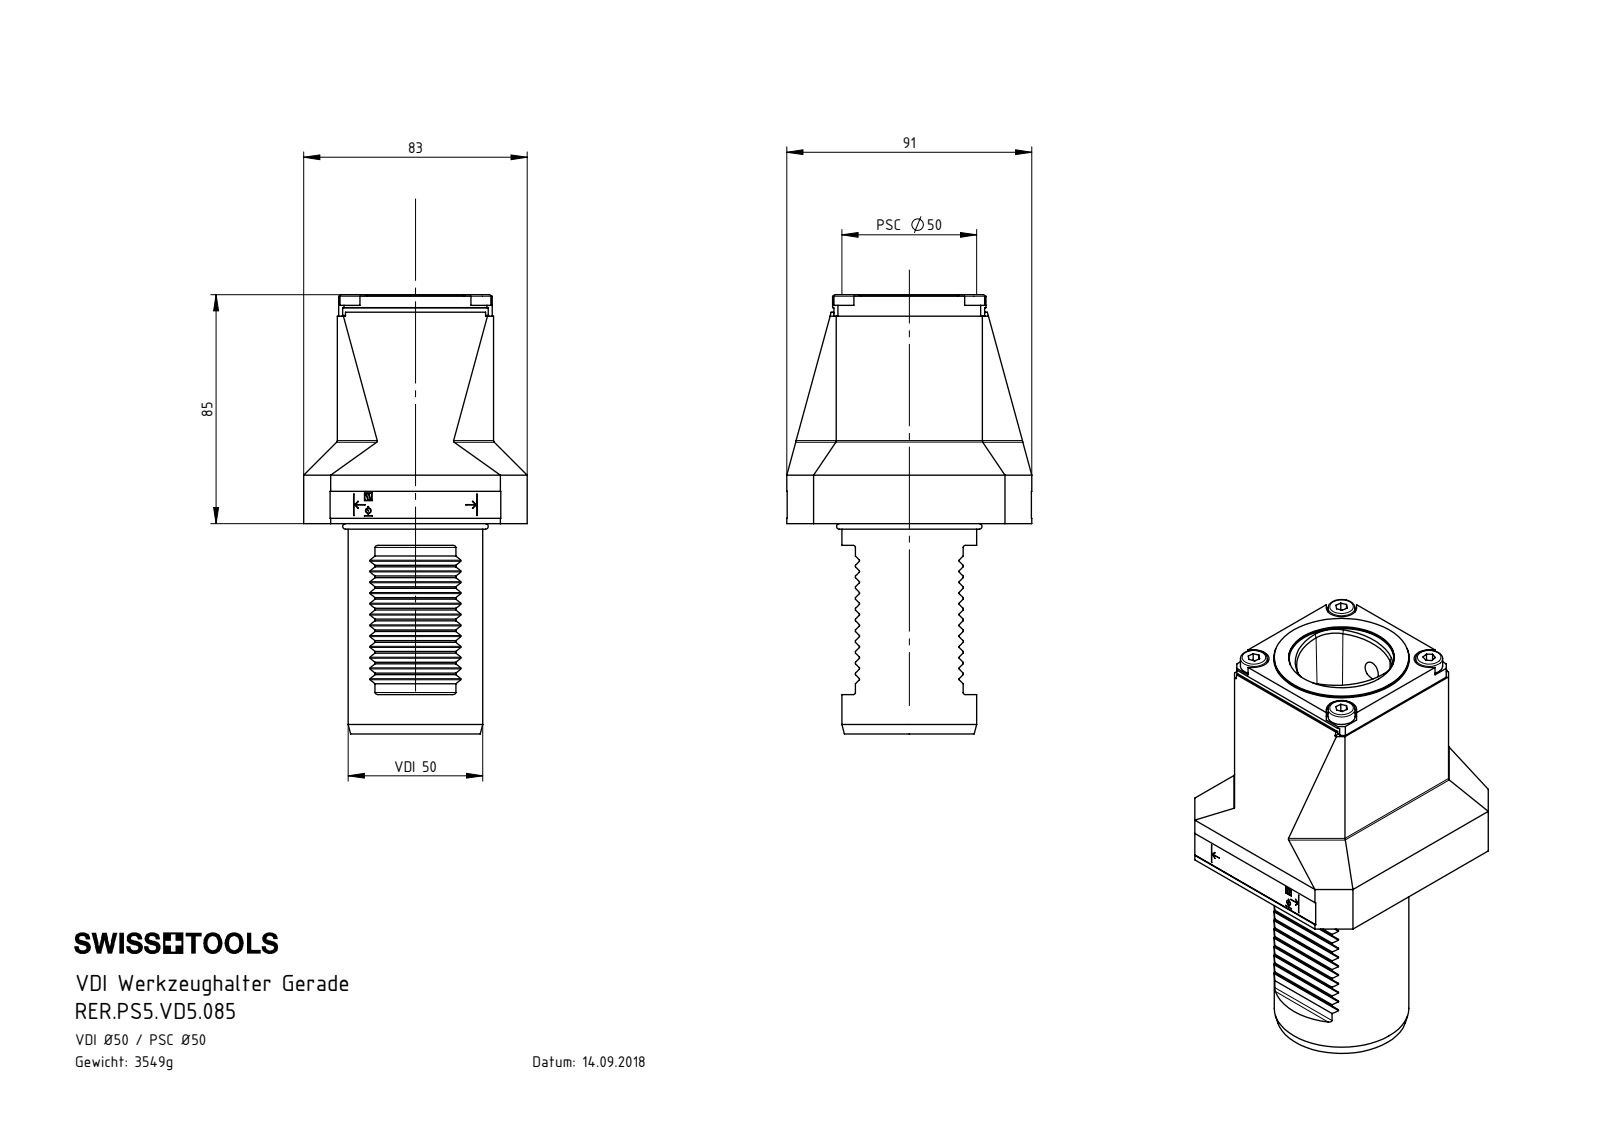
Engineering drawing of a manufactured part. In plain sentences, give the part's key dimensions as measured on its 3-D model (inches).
The part is named "ISO 4762 - M4 x 30_PreviewCfg; VD5-ER1.016.010_A; DIN 3771 - 13x1.5; DIN 3771 - 48x1.5_vorgespannt (+8 more)". Its 3-D file was written by "SolidWorks 2022 (AUTOMOTIVE_DESIGN)". It is 23 solids with 916 faces: 400 planar, 236 cylindrical and 280 other. Overall it measures 6.417 by 3.583 by 3.268 inches. Its volume is 29.76 cubic inches and its surface area 181.1 square inches. Round holes: 5 of diameter 0.197, 4 of diameter 0.244, 4 of diameter 0.268, 2 of diameter 0.13, 2 of diameter 0.157, 2 of diameter 0.165, 2 of diameter 0.551, 1 of diameter 0.083, 1 of diameter 0.098, 1 of diameter 0.236, 1 of diameter 0.276, 1 of diameter 0.354. Round bosses or shafts: 5 of diameter 0.394, 4 of diameter 0.236, 2 of diameter 0.787, 2 of diameter 0.276, 2 of diameter 0.157, 1 of diameter 1.969, 1 of diameter 1.957, 1 of diameter 1.843. Partial cylindrical surfaces (rounded edges, fillets, slot ends): 24 of radius 0.012, 10 of radius 0.031, 6 of radius 0.004, 4 of radius 0.177, 4 of radius 0.22, 2 of radius 0.008, 2 of radius 0.128, 2 of radius 0.157. The main face-to-face distances are 0.118, 1.063, 2.283, 3.031, 2.244, 0.945, 0.492, 2.776, 2.913, 0.787. The hole center spacings are 0.962, 1.281, 1.74, 1.811, 0.398, 0.581, 0.591, 0.77.
